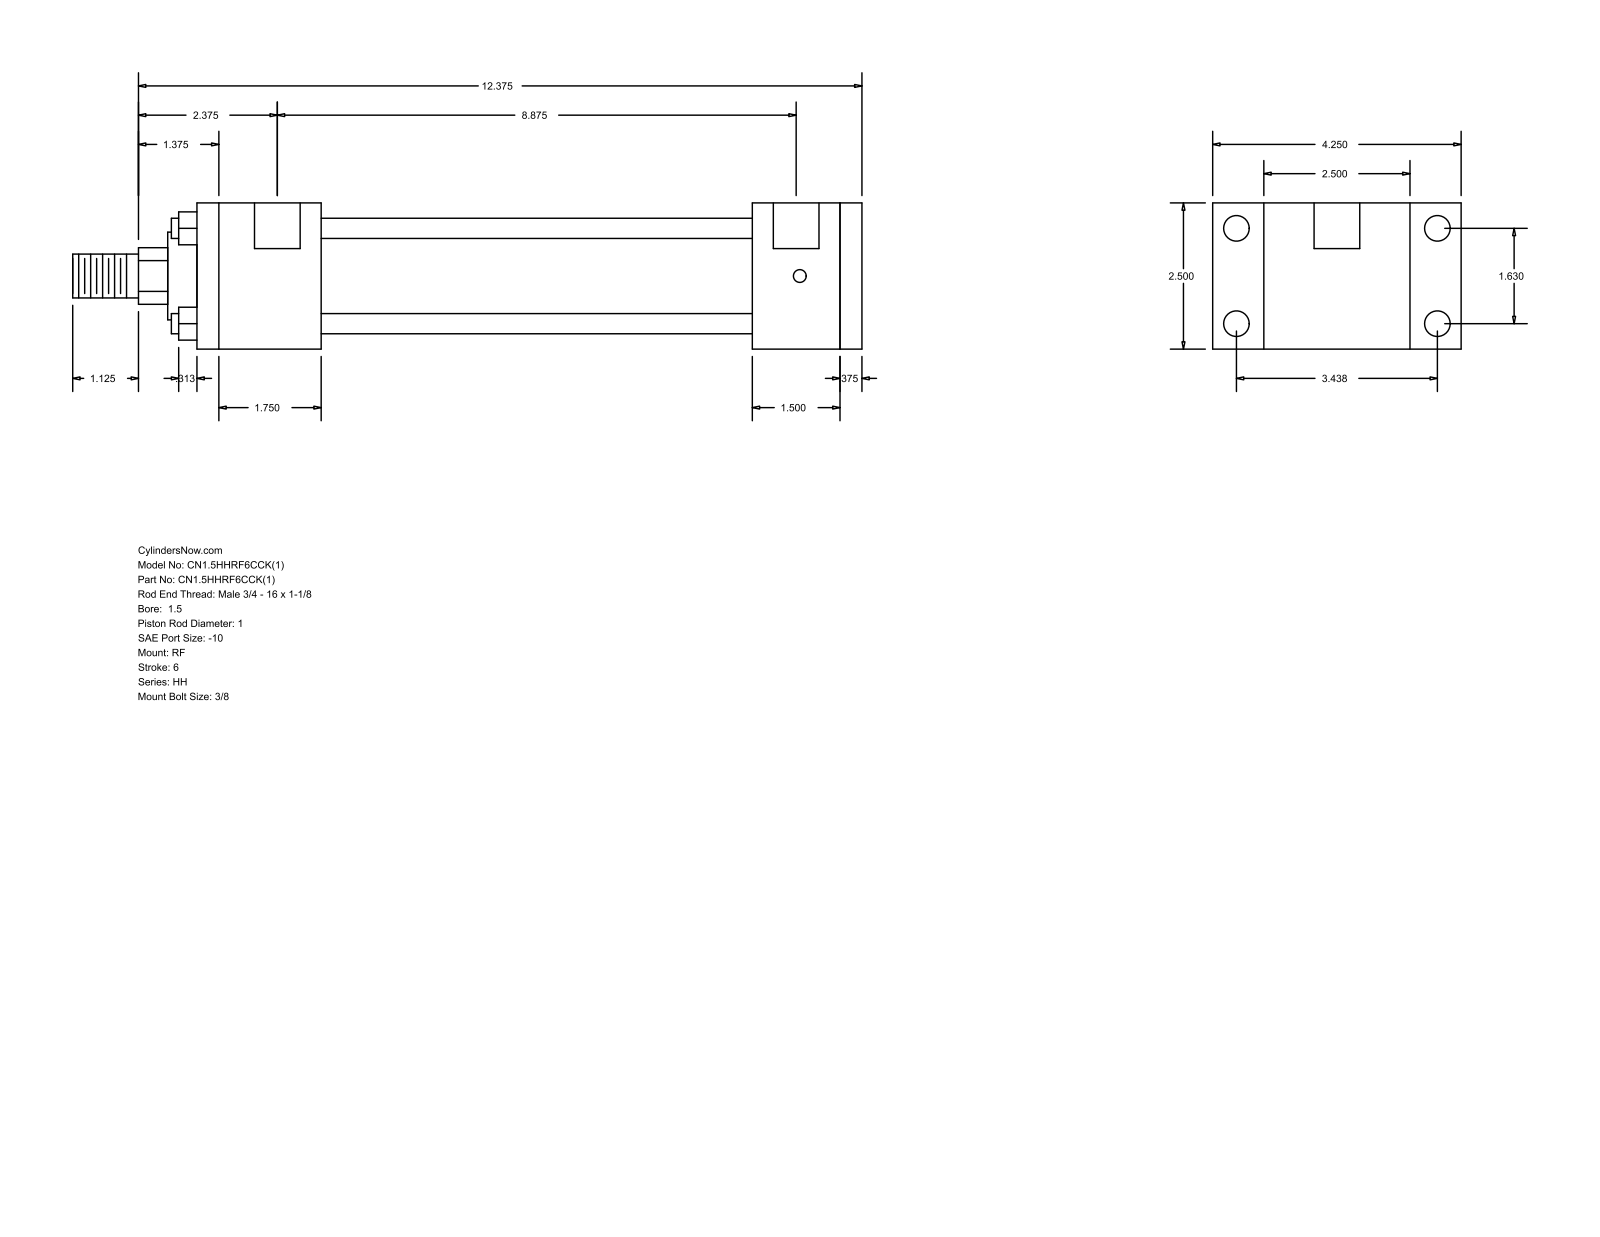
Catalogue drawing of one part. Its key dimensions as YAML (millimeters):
part_name: "HH_RF__0150_1"
step_written_by: "GSSL Pune (CONFIG_CONTROL_DESIGN)"
units: millimeters
bodies: {solids: 0, faces: 92, planar: 64, cylindrical: 28, other: 0}
overall_size: [342.9, 107.95, 63.5]
round_holes:
  - {diameter: 5.56, count: 4}
  - {diameter: 11.13, count: 4}
  - {diameter: 19.84, count: 2}
round_bosses_or_shafts:
  - {diameter: 8.76, count: 4}
  - {diameter: 44.45, count: 1}
  - {diameter: 38.1, count: 1}
  - {diameter: 25.4, count: 1}
  - {diameter: 19.05, count: 1}
partial_cylinders:
  - {radius: 12.29, count: 1}
face_to_face_distances: [63.5, 9.52, 38.1, 187.32, 225.42, 234.94, 47.62, 53.98, 241.3, 279.4]
hole_center_spacings: [1.59, 41.4, 87.32, 96.64, 227.01, 228.6, 225.42]
